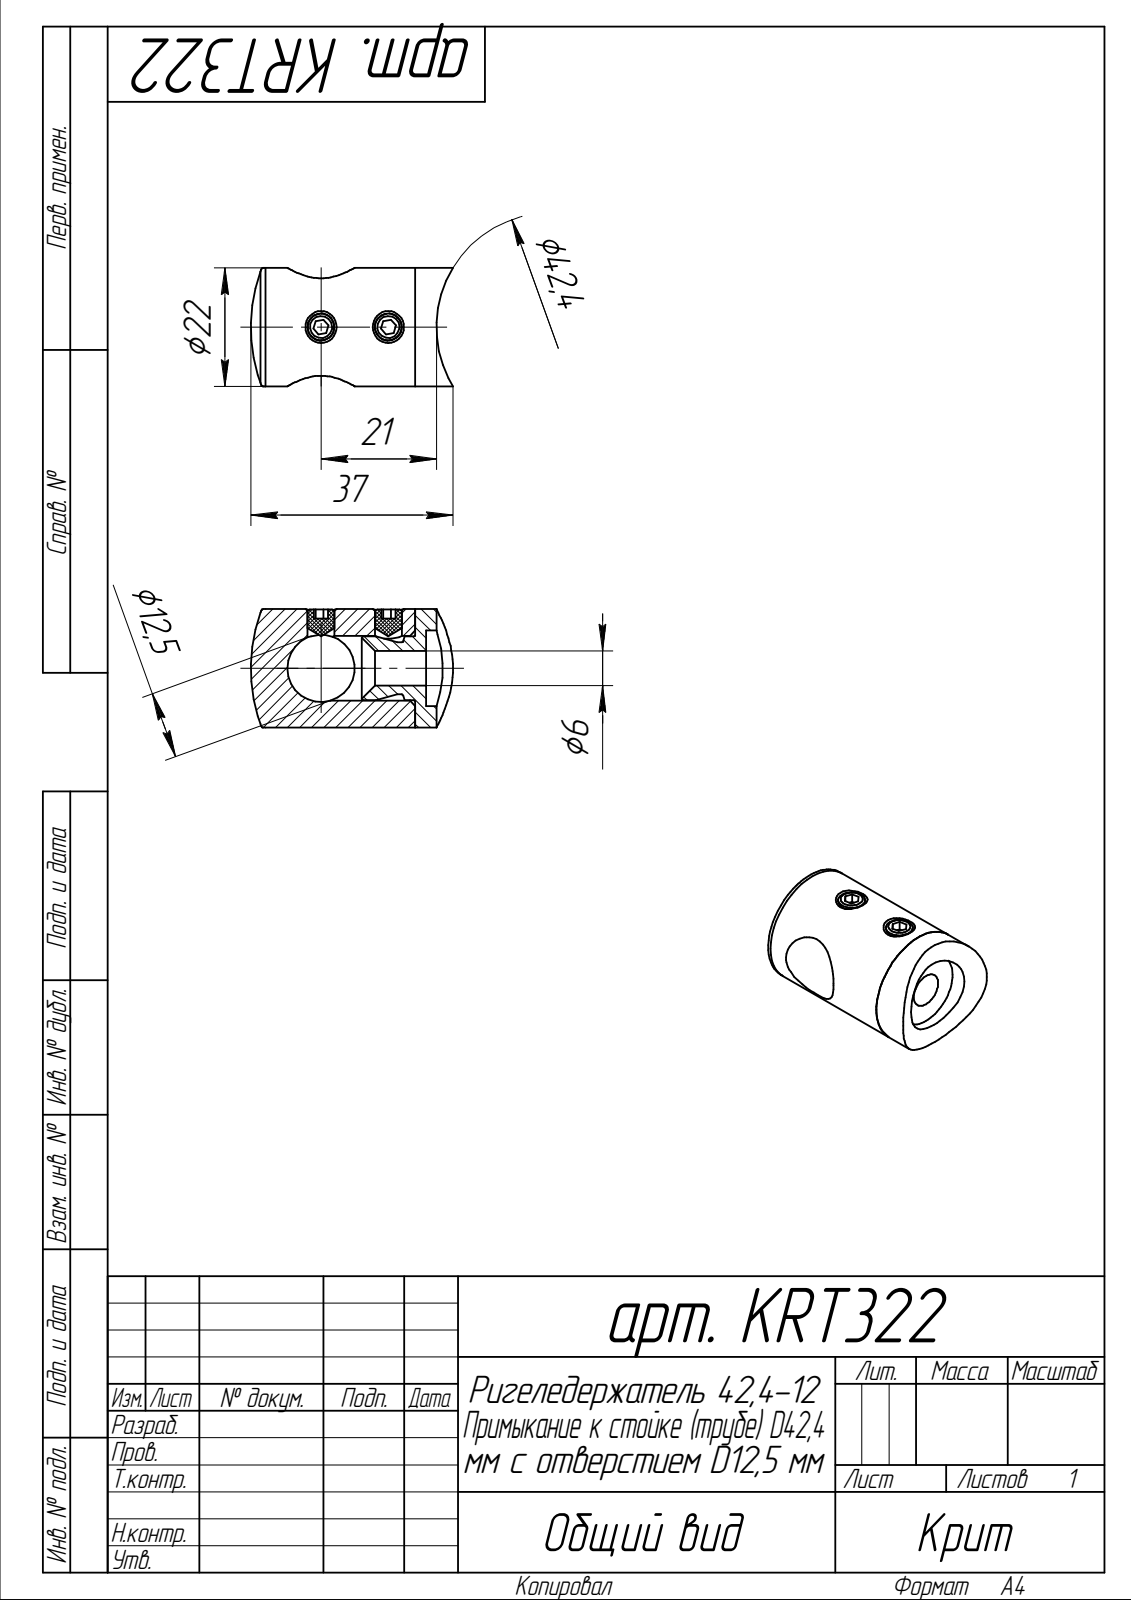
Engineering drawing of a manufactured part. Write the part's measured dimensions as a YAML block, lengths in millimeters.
part_name: "socket set screw cone point_am_B18.3.6M - M5 x 0.8 x 5 Hex Socket Cone Pt. SS --N; арт. KRT322.001; арт. KRT322.002; арт. KRT322"
step_written_by: "SolidWorks 2014 (AUTOMOTIVE_DESIGN)"
units: millimeters
bodies: {solids: 4, faces: 78, planar: 21, cylindrical: 27, other: 30}
overall_size: [37.5, 22, 22]
volume: 9128
surface_area: 5564
round_holes:
  - {diameter: 5, count: 2}
  - {diameter: 6.4, count: 1}
  - {diameter: 12, count: 1}
  - {diameter: 12.5, count: 1}
  - {diameter: 14, count: 1}
round_bosses_or_shafts:
  - {diameter: 22, count: 1}
  - {diameter: 11.8, count: 1}
  - {diameter: 9.7, count: 1}
partial_cylinders:
  - {radius: 21.2, count: 1}
face_to_face_distances: [2, 2.5, 1.7, 11.86, 2.52, 9.34, 14.36, 9.36, 5.02, 11.84]
hole_center_spacings: [12.5]
